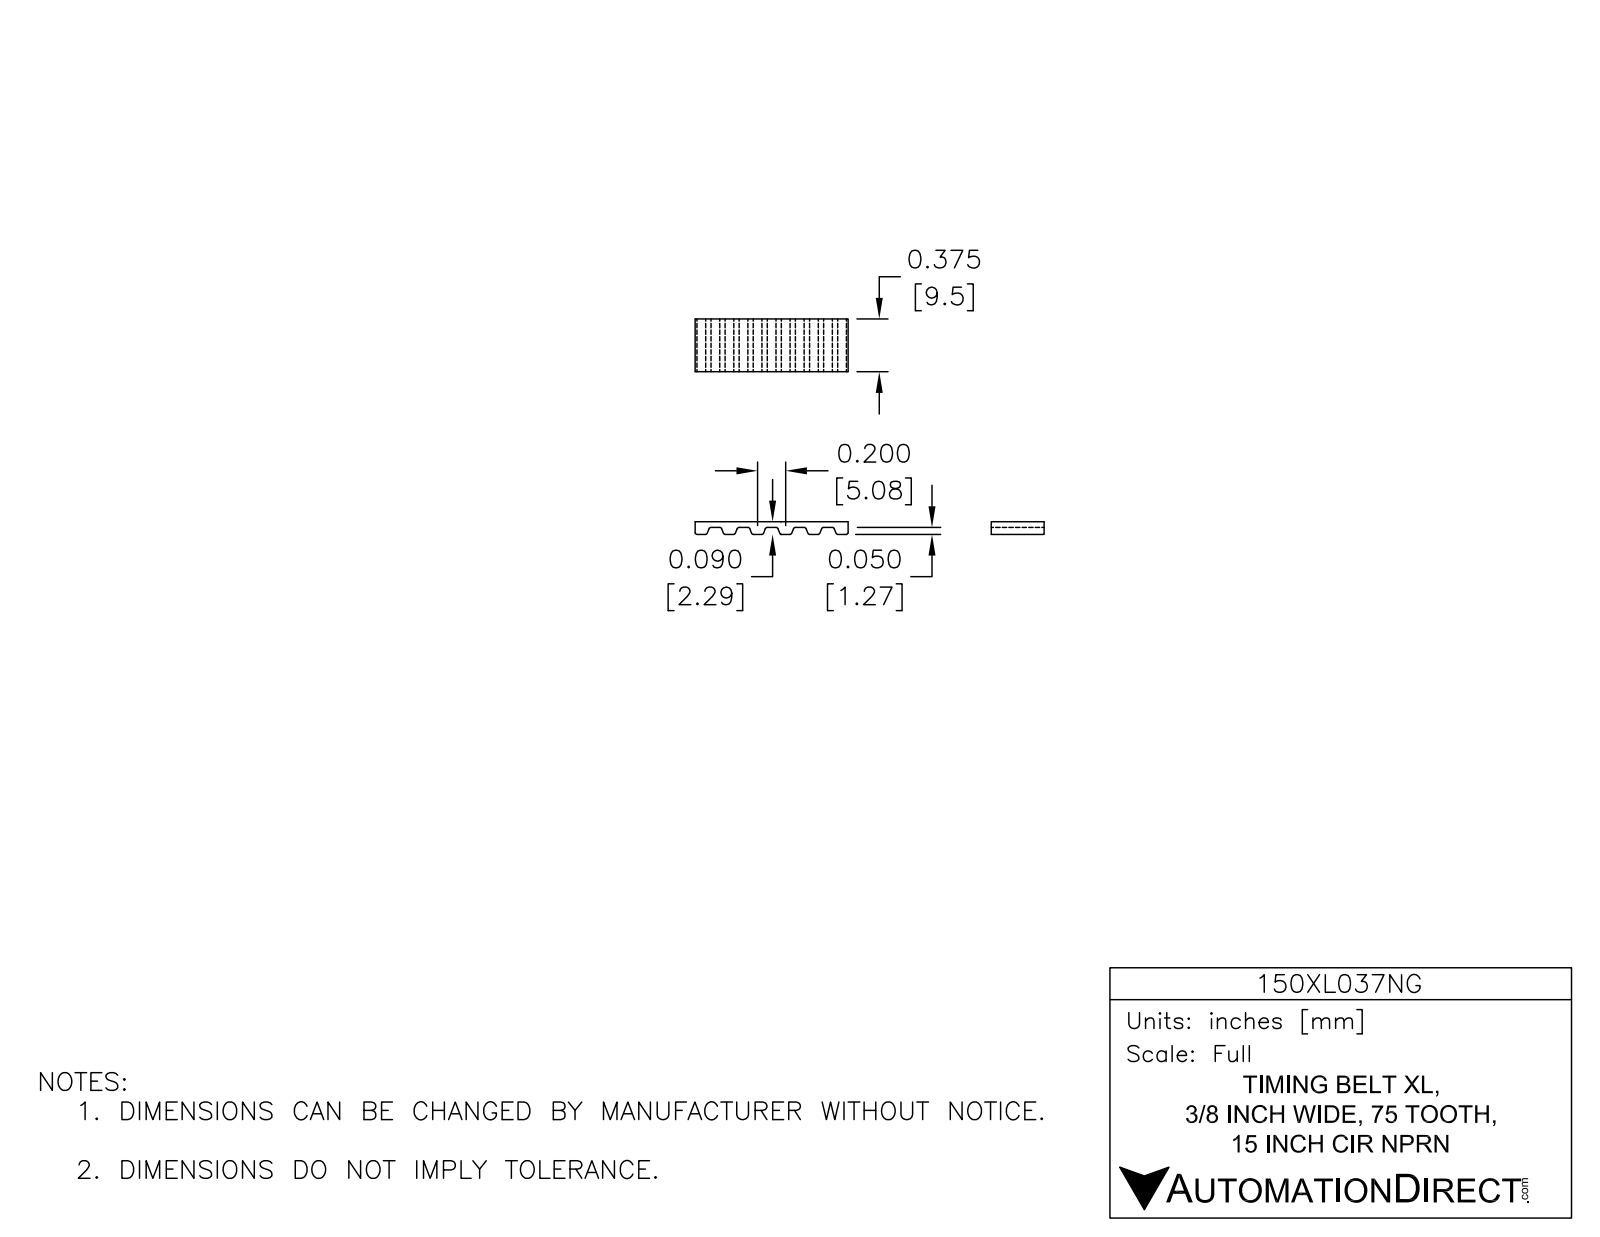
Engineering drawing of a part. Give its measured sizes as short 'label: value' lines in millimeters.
name: 150XL037NG
written by: SolidWorks 2014 (AUTOMOTIVE_DESIGN)
unit: mm
bodies: 1 solid, 640 faces (258 planar, 382 cylindrical, 0 other)
size: 147 × 76.2 × 9.5
volume: 5 000 mm³; area: 9 252 mm²
rounds: 300× R0.4, 2× R37.1, 2× R38.1
face distances: 76.2, 1, 75.2, 9.5, 74.2, 9, 18.1, 4.5, 13.6, 27.2
